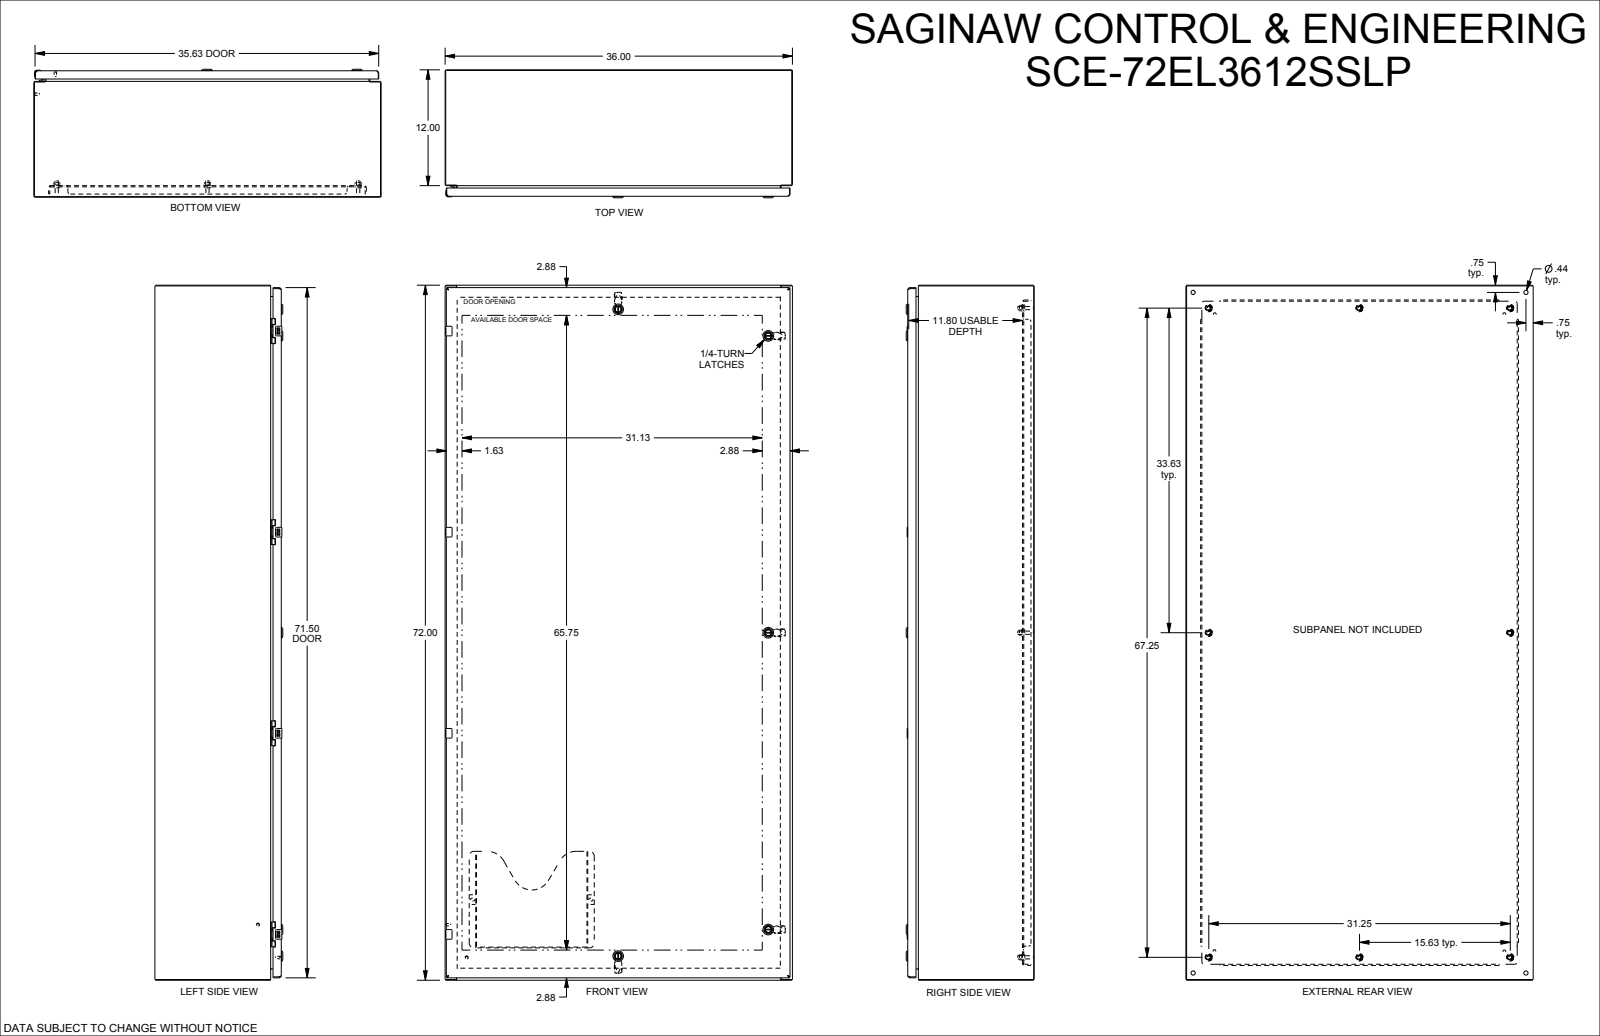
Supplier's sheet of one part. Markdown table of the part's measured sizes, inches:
| quantity | value |
| --- | --- |
| part name | SCE-72EL3612SSLP |
| STEP written by | SolidWorks 2019 (CONFIG_CONTROL_DESIGN) |
| units | inches |
| bodies | 0 solids, 5420 faces (2661 planar, 1535 cylindrical, 1224 other) |
| overall size | 72 × 36 × 13.256 |
| round holes (diameter × count) | 0.394 × 15, 0.172 × 8, 0.205 × 8, 0.244 × 8, 0.266 × 8, 0.367 × 8, 0.375 × 8, 0.5 × 8, 0.197 × 5, 0.315 × 5, 0.634 × 5, 0.156 × 4 |
| round bosses / shafts (diameter × count) | 0.17 × 12, 0.366 × 8, 0.332 × 8, 0.25 × 8, 1.102 × 5, 0.866 × 5, 0.802 × 5, 0.78 × 5 |
| partial cylindrical surfaces (radius × count) | 0.012 × 142, 0.01 × 52, 0.02 × 52, 0.015 × 48, 0.04 × 23, 0.157 × 20, 0.03 × 17, 0.031 × 16 |
| main face-to-face distances | 0.075, 0.104, 12.92, 12.995, 1, 13.099, 13.024, 1.125, 11.795, 11.92 |
| hole center spacings | 2.461, 20.833, 41.667, 1.274, 4.754, 3.48, 4.262, 20.833 |
